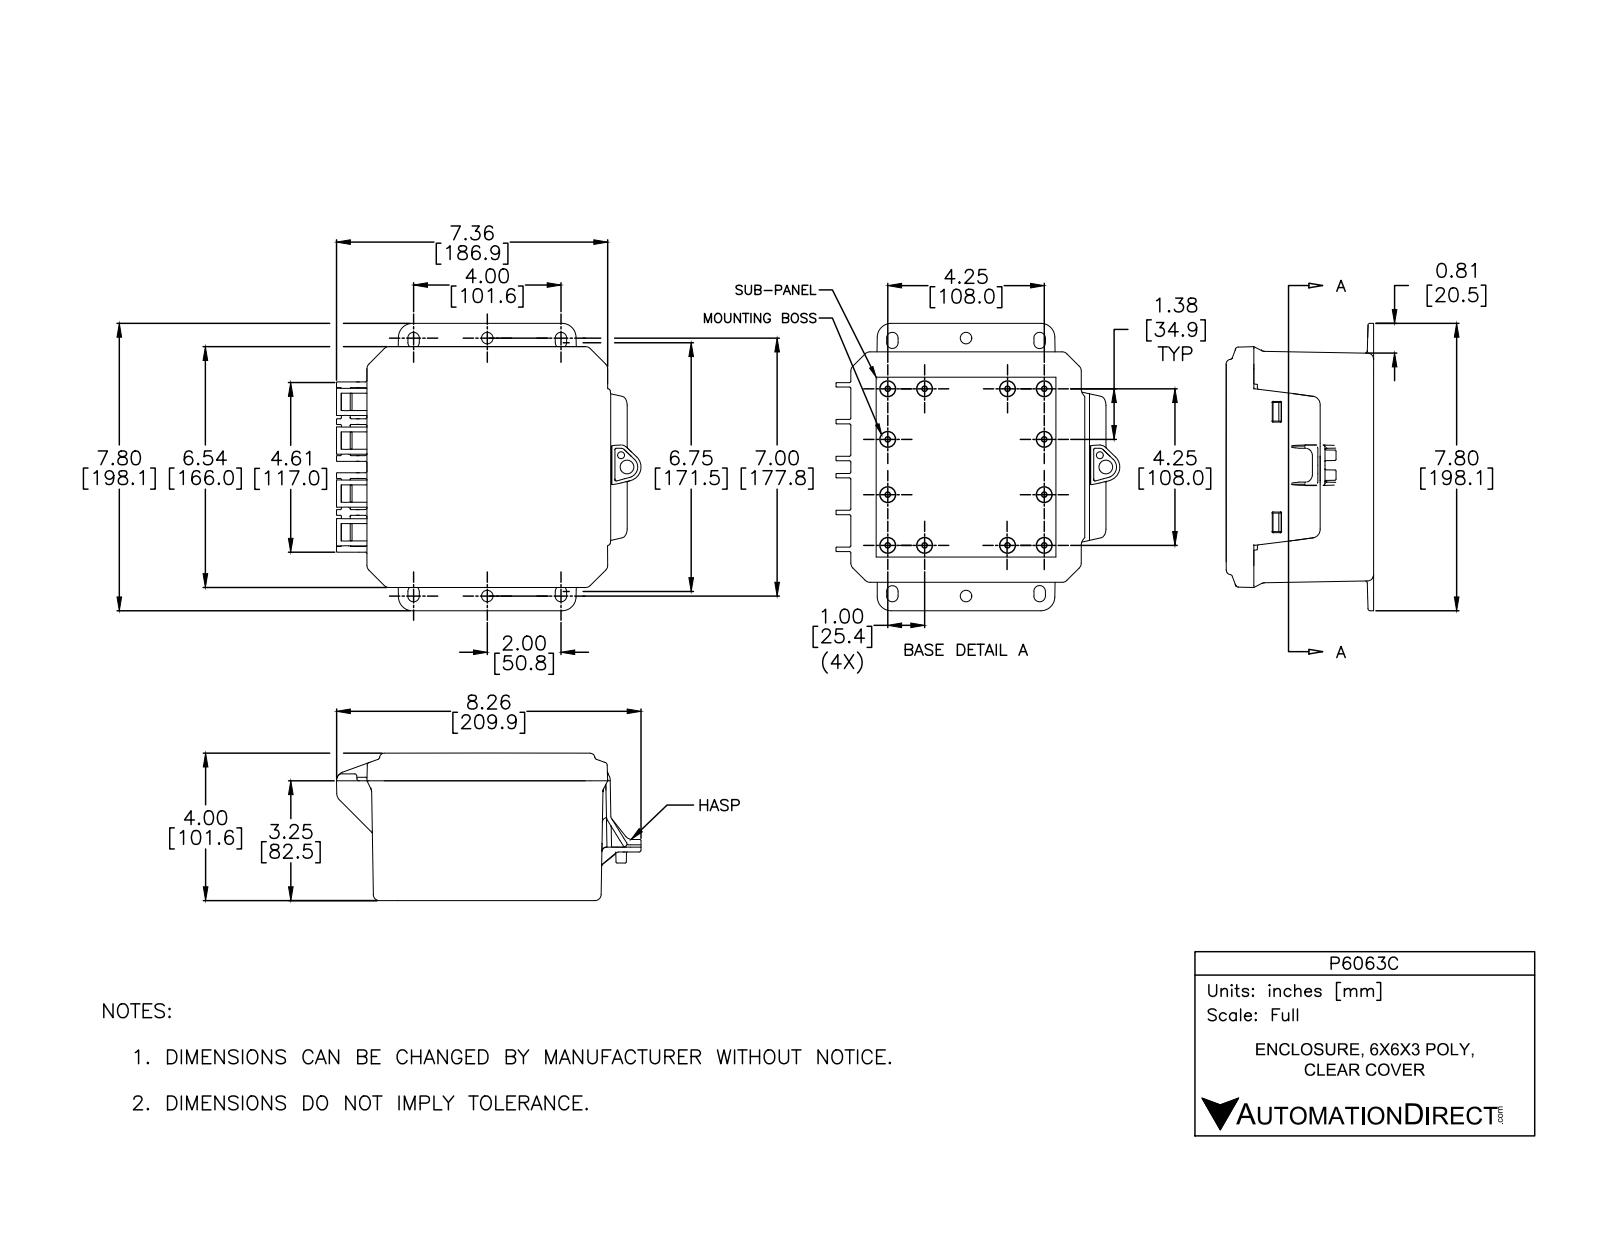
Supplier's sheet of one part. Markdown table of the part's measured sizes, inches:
| quantity | value |
| --- | --- |
| part name | P6063C; 6X6X3-BOX-SD-HINGE-INT-LATCH; 6X6X3-LID-SD-HINGE-INT-LATCH |
| STEP written by | SolidWorks 2016 (AUTOMOTIVE_DESIGN) |
| units | inches |
| bodies | 1 solid, 2260 faces (577 planar, 802 cylindrical, 881 other) |
| overall size | 8.266 × 7.8 × 4.005 |
| volume | 10.63 in³ |
| surface area | 440.8 in² |
| round holes (diameter × count) | 0.14 × 12, 0.12 × 1 |
| round bosses / shafts (diameter × count) | 0.242 × 1 |
| partial cylindrical surfaces (radius × count) | 0.02 × 123, 0.03 × 118, 0.015 × 63, 0.04 × 54, 0.06 × 32, 0.01 × 31, 0.19 × 17, 0.08 × 12 |
| main face-to-face distances | 0.15, 5.712, 0.472, 6.363, 6.213, 6.184, 0.374, 3.25, 3.1, 1 |
| hole center spacings | 4.25, 1, 1.375, 1.7, 2.875, 3.044, 3.25, 3.528 |
